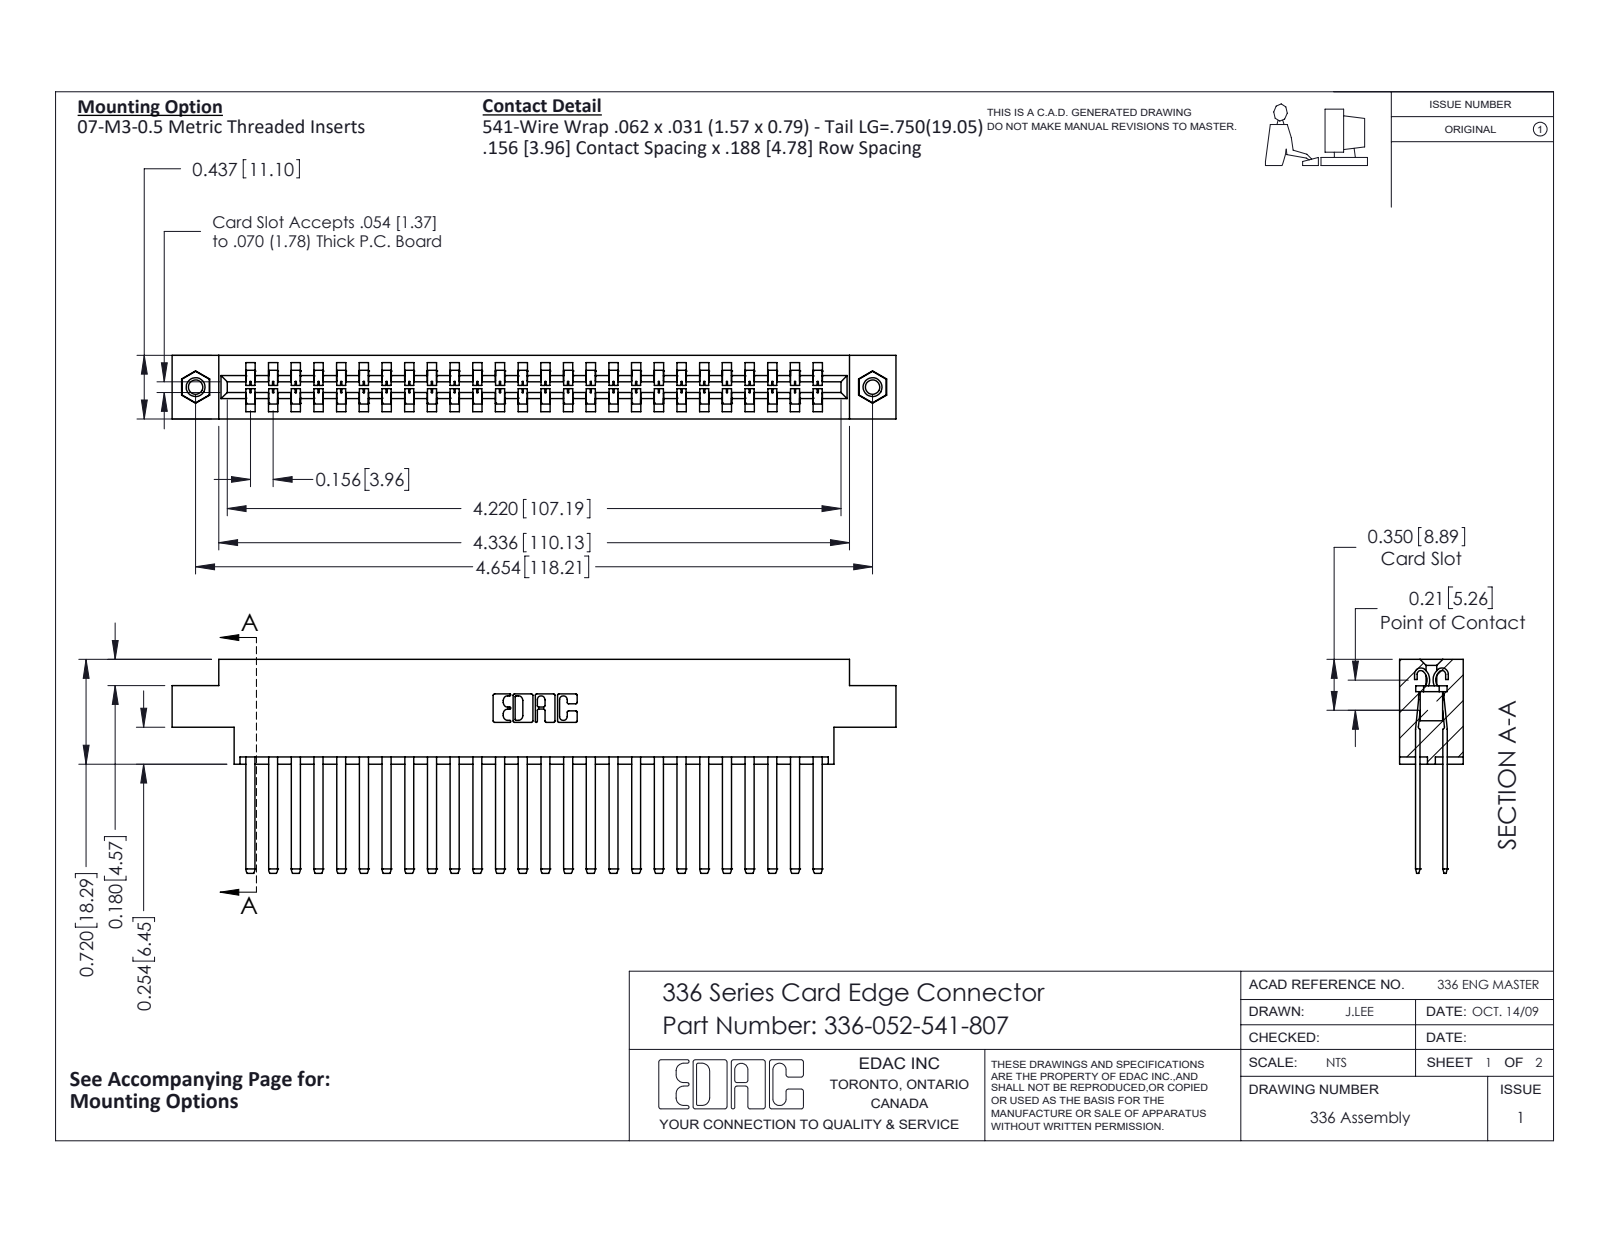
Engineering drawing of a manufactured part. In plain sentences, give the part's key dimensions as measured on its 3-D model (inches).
The part is named "336-052-541-807; 345-250-001_345-250-005-103; 336 Part_Offset - .156 Dia - TI; 336-290-001_336-290-541". Its 3-D file was written by "SolidWorks 2020 (CONFIG_CONTROL_DESIGN)". It is 55 solids with 2362 faces: 1458 planar, 888 cylindrical and 16 other. Overall it measures 4.977 by 1.47 by 0.437 inches. Its volume is 1.159 cubic inches and its surface area 37.36 square inches. Round holes: 2 of diameter 0.098, 2 of diameter 0.125, 2 of diameter 0.156. Round bosses or shafts: 2 of diameter 0.155. Partial cylindrical surfaces (rounded edges, fillets, slot ends): 104 of radius 0.004, 52 of radius 0.056, 22 of radius 0.01, 6 of radius 0.007, 6 of radius 0.031, 4 of radius 0.022, 4 of radius 0.04, 3 of radius 0.026. The main face-to-face distances are 0.188, 0.328, 0.14, 0.297, 0.109, 0.031, 0.437, 0.033, 0.181, 0.146. The hole center spacings are 4.654.
